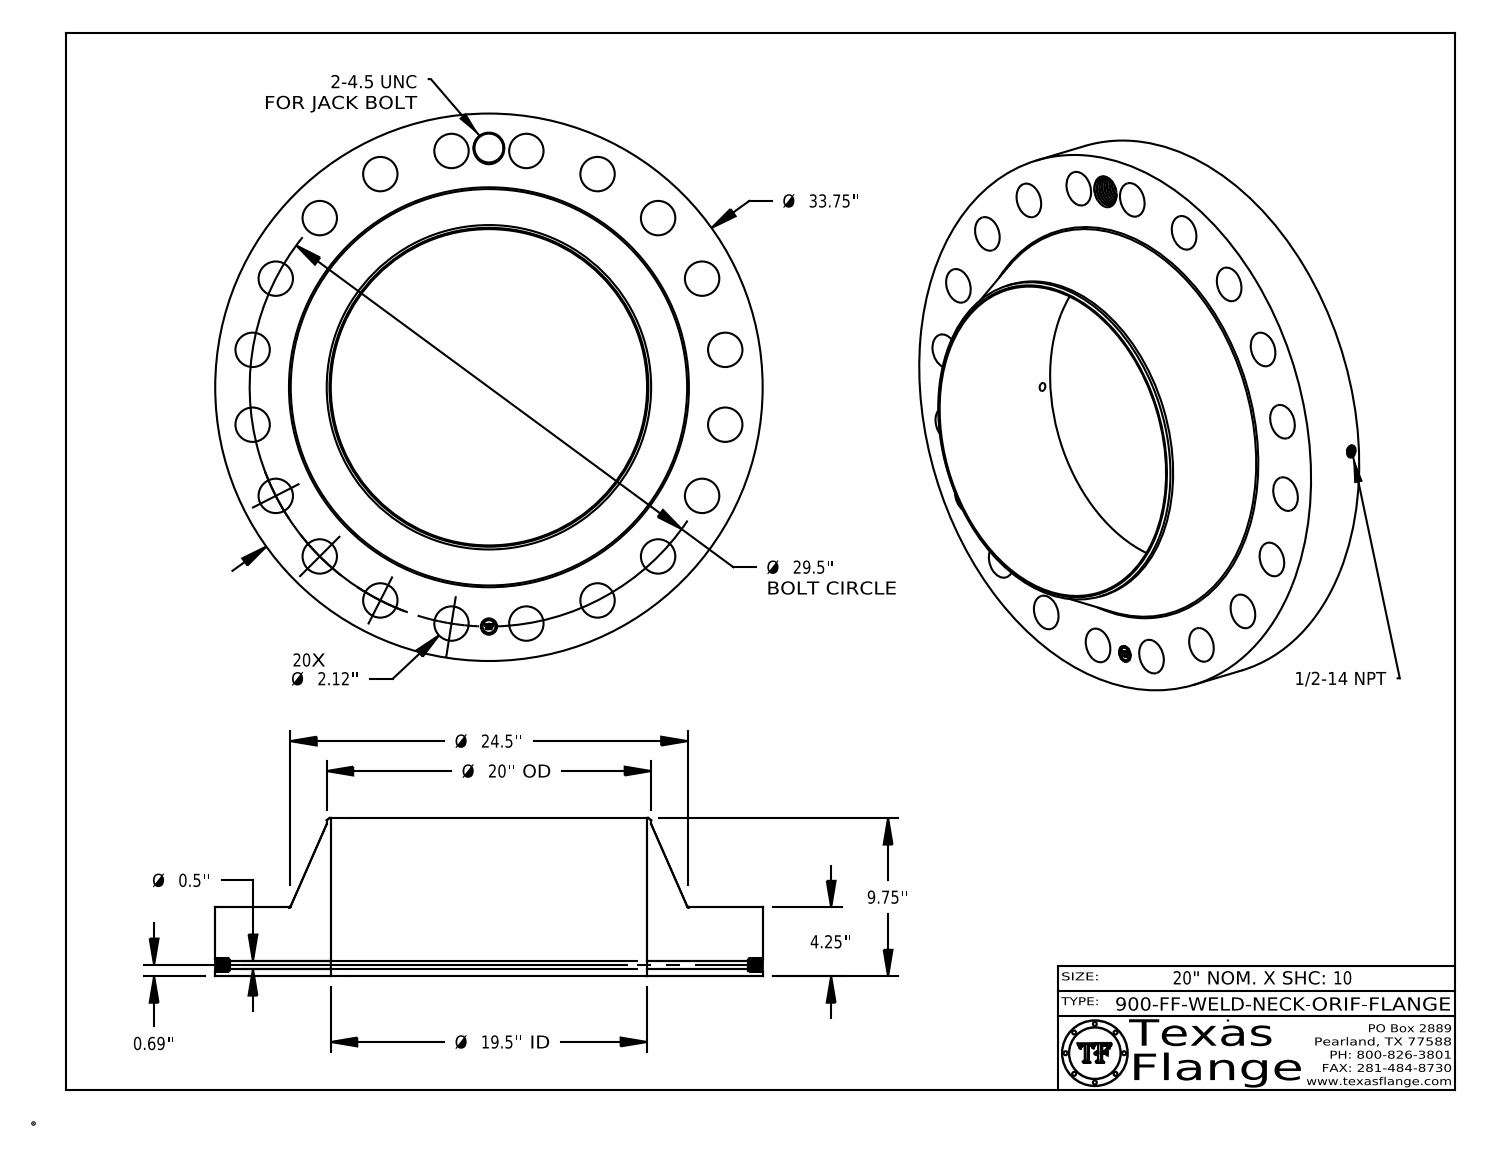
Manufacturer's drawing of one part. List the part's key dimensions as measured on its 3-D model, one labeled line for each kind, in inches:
Part name (STEP PRODUCT): 900-FF-WELD-NECK
STEP written by: CATIA V5 STEP AP214 (AUTOMOTIVE_DESIGN)
Units: inches
Bodies: 1 solid, 815 faces (368 planar, 124 cylindrical, 323 other)
Overall size (bounding box): 33.75 × 33.75 × 9.75
Volume: 2 692 in³ · Surface area: 2 971 in²
Round holes (diameter × count): ⌀2.12 ×20, ⌀0.5 ×1, ⌀0.672 ×1, ⌀1 ×1, ⌀1.781 ×1, ⌀19.5 ×1
Round bosses / shafts (diameter × count): ⌀0.061 ×8, ⌀33.75 ×1, ⌀20 ×1, ⌀0.788 ×1
Main face-to-face distances: 4.25, 9.75, 5.5, 4.235, 0.015, 5.515, 0.298, 0.293, 0.054, 0.248
Hole centre spacings: 4.615, 9.116, 13.393, 17.34, 20.86, 23.866, 26.285, 29.137
